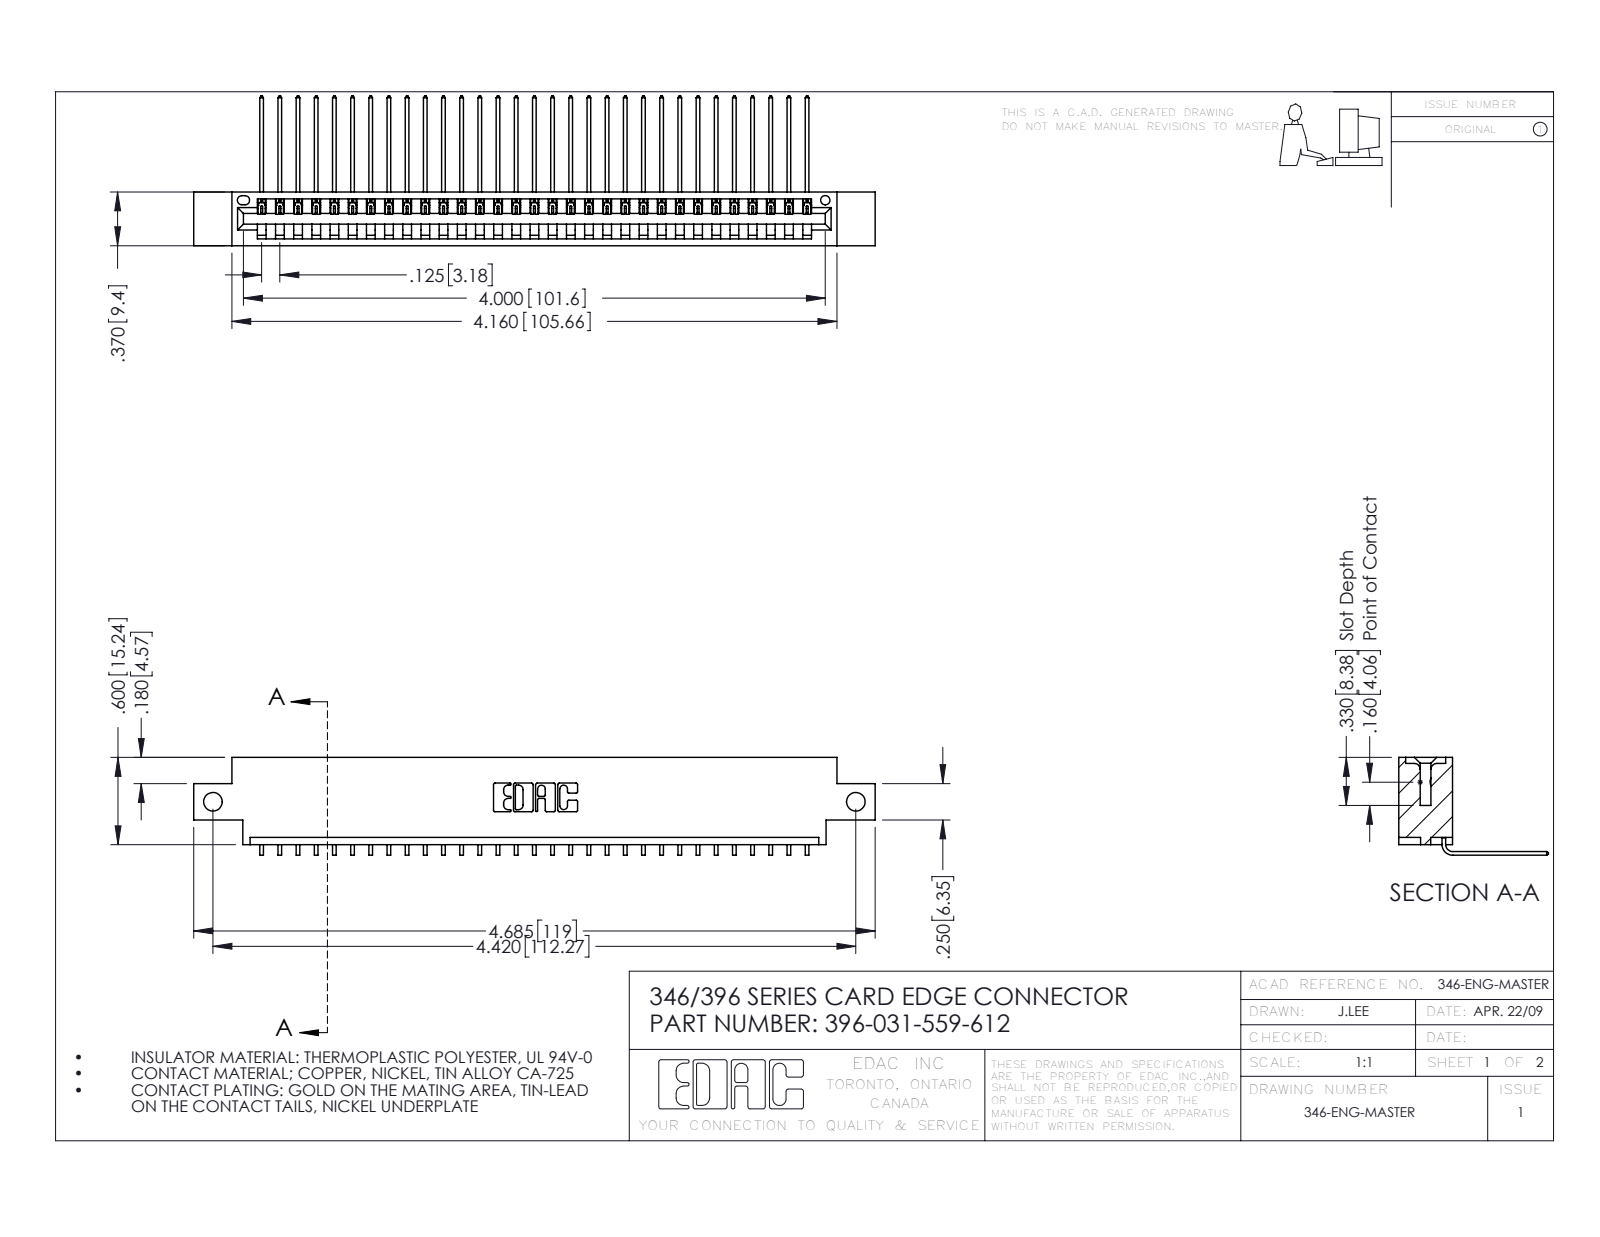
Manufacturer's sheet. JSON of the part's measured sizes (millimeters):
{"part_name": "396-031-559-612; 345-292-001_558 559 Tail - 1; 346 Part_0.170 Offset - Side Mount", "step_written_by": "SolidWorks 2016 (CONFIG_CONTROL_DESIGN)", "units": "millimeters", "bodies": {"solids": 32, "faces": 1986, "planar": 1382, "cylindrical": 604, "other": 0}, "overall_size": [119, 26.2, 17.1], "volume_mm3": 11200, "surface_area_mm2": 14480, "round_holes": [[3.3, 2], [1.6, 1]], "partial_cylinders_radius": [[0.2, 62], [0.3, 22], [0.2, 6], [0.8, 6], [0.7, 3], [0.8, 2], [1, 2], [0.4, 1]], "face_to_face_distances": [1.2, 8.2, 9.4, 6.4, 0.6, 1.8, 7.6, 3.8, 5.6, 2.5], "hole_center_spacings": [112.3]}
